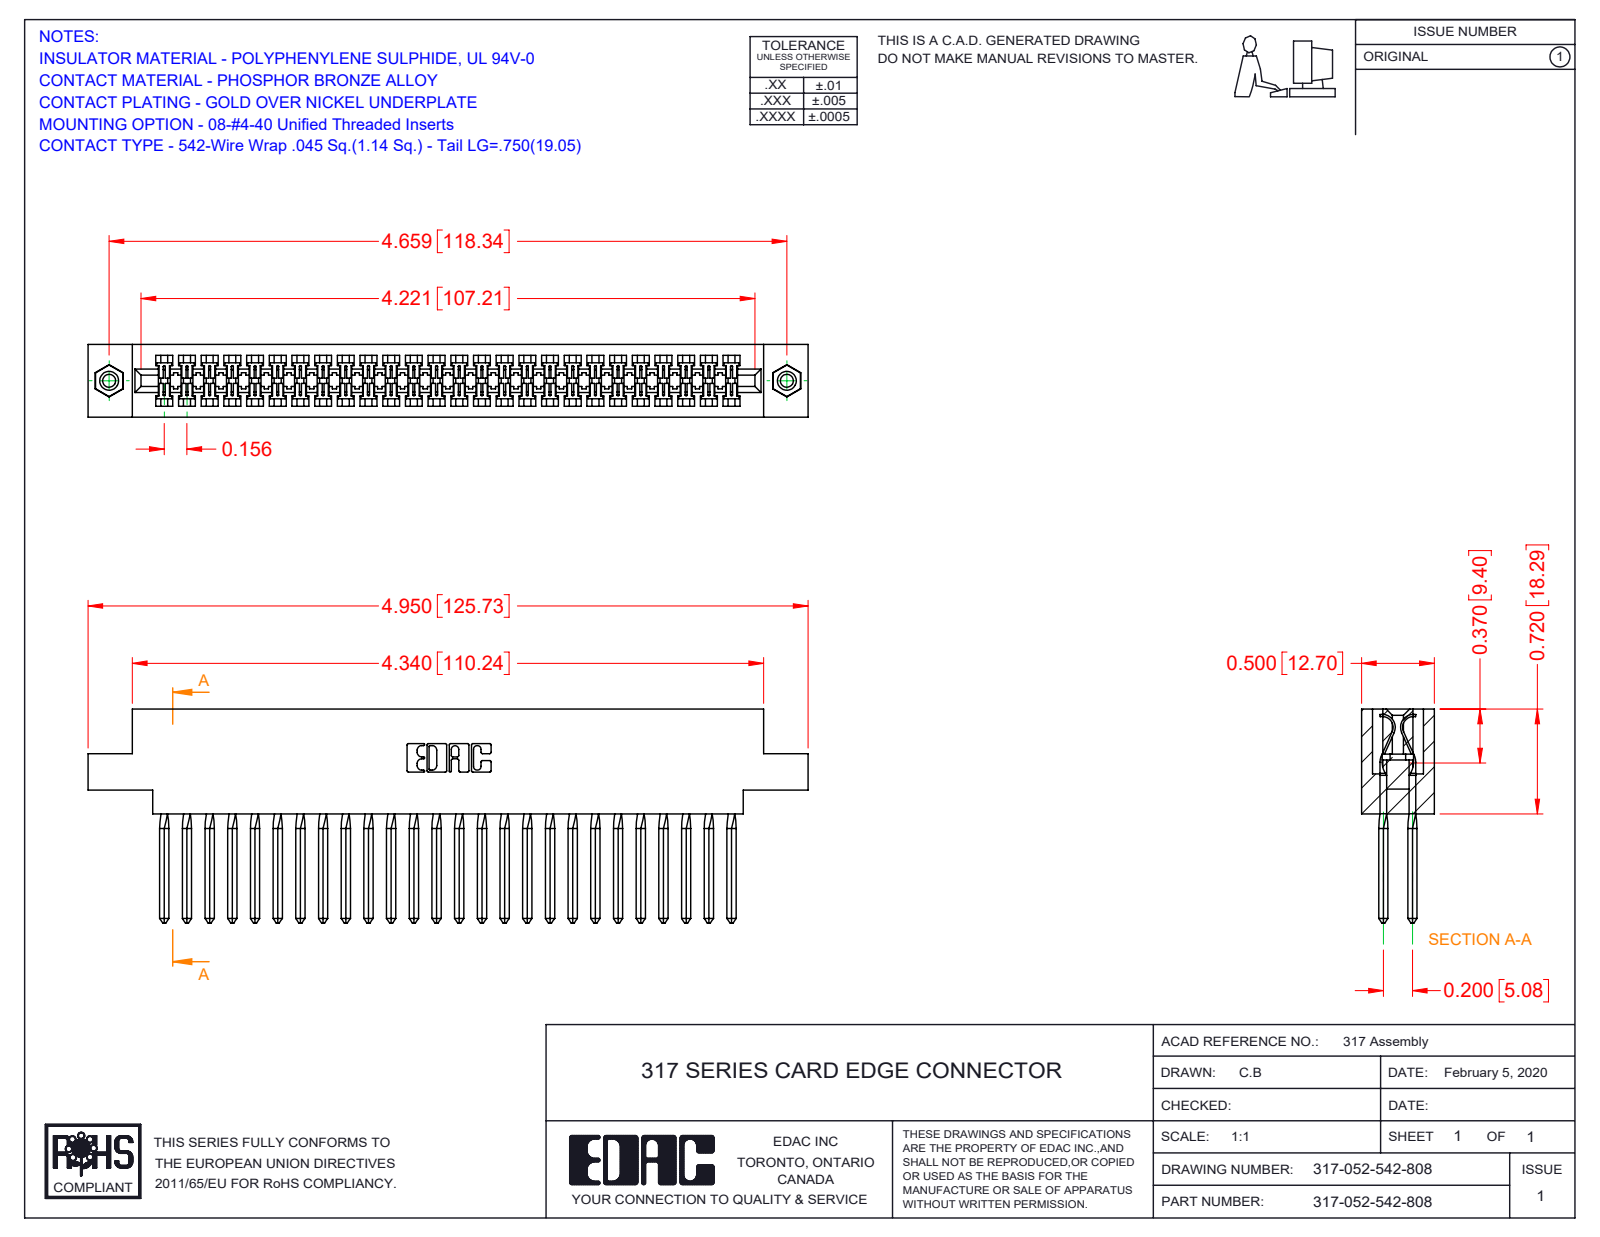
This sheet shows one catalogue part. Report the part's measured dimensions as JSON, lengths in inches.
{"part_name": "317-052-542-878; 317-290-003_542; 345-250-001_345-250-003-102; 317 Part_.156 Dia - TI", "step_written_by": "SolidWorks 2016 (CONFIG_CONTROL_DESIGN)", "units": "inches", "bodies": {"solids": 55, "faces": 3126, "planar": 2482, "cylindrical": 420, "other": 224}, "overall_size": [4.95, 1.47, 0.5], "volume_in3": 1.225, "surface_area_in2": 42.51, "round_holes": [[0.089, 2], [0.125, 2], [0.156, 2]], "round_bosses_or_shafts": [[0.155, 2]], "partial_cylinders_radius": [[0.006, 104], [0.01, 22], [0.007, 6], [0.031, 6], [0.026, 3], [0.074, 2], [0.089, 2], [0.1, 2]], "face_to_face_distances": [0.5, 0.075, 0.425, 0.35, 0.2, 0.11, 0.116, 0.136, 0.046, 0.72], "hole_center_spacings": [4.659]}
